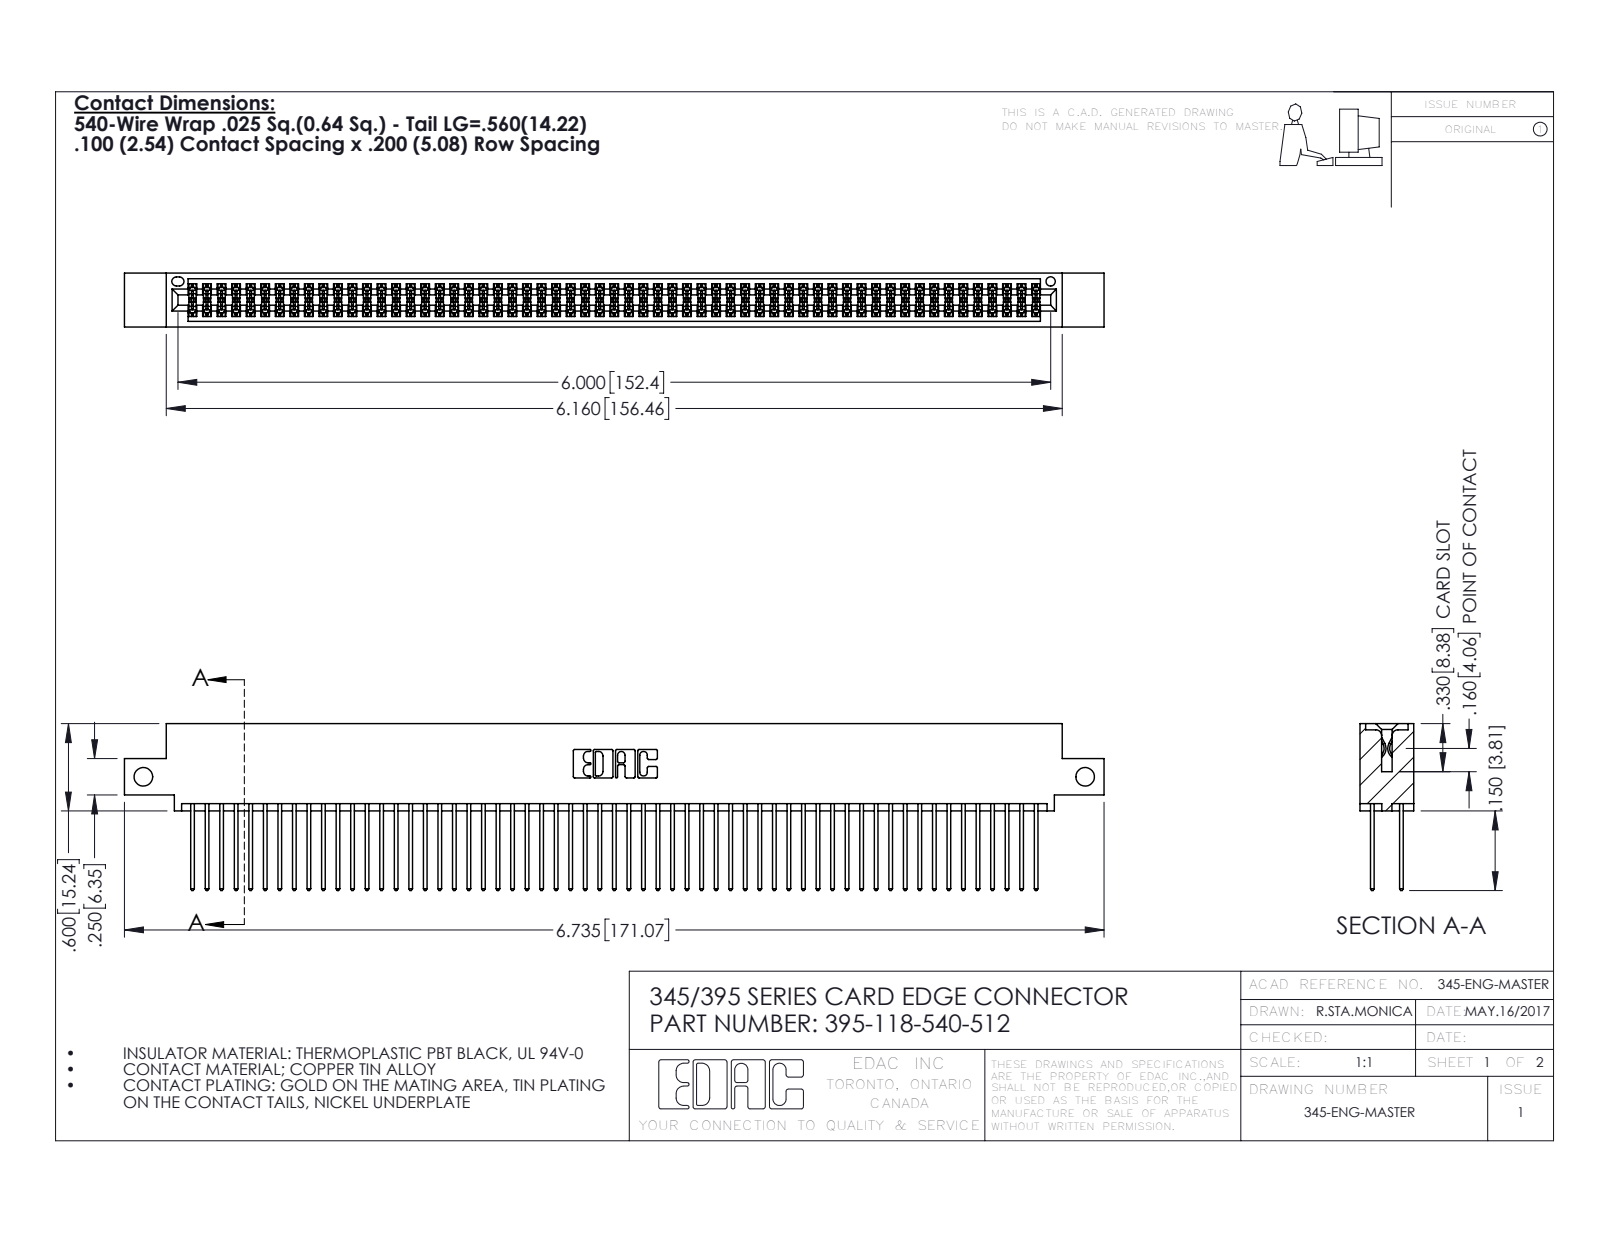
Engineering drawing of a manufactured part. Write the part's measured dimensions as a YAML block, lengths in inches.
part_name: "345 Part_0.110 Offset - Side Mount; 395-118-540-512; 345-292-001_345-293-140"
step_written_by: "SolidWorks 2016 (CONFIG_CONTROL_DESIGN)"
units: inches
bodies: {solids: 119, faces: 6030, planar: 3978, cylindrical: 2052, other: 0}
overall_size: [6.735, 1.147, 0.37]
volume: 1.041
surface_area: 42.75
round_holes:
  - {diameter: 0.128, count: 2}
  - {diameter: 0.064, count: 1}
partial_cylinders:
  - {radius: 0.006, count: 177}
  - {radius: 0.01, count: 118}
  - {radius: 0.01, count: 22}
  - {radius: 0.007, count: 6}
  - {radius: 0.031, count: 6}
  - {radius: 0.026, count: 3}
  - {radius: 0.014, count: 2}
  - {radius: 0.019, count: 2}
face_to_face_distances: [0.298, 0.072, 0.2, 0.098, 0.272, 0.025, 0.225, 0.37, 0.175, 0.149]
hole_center_spacings: [6.475]
